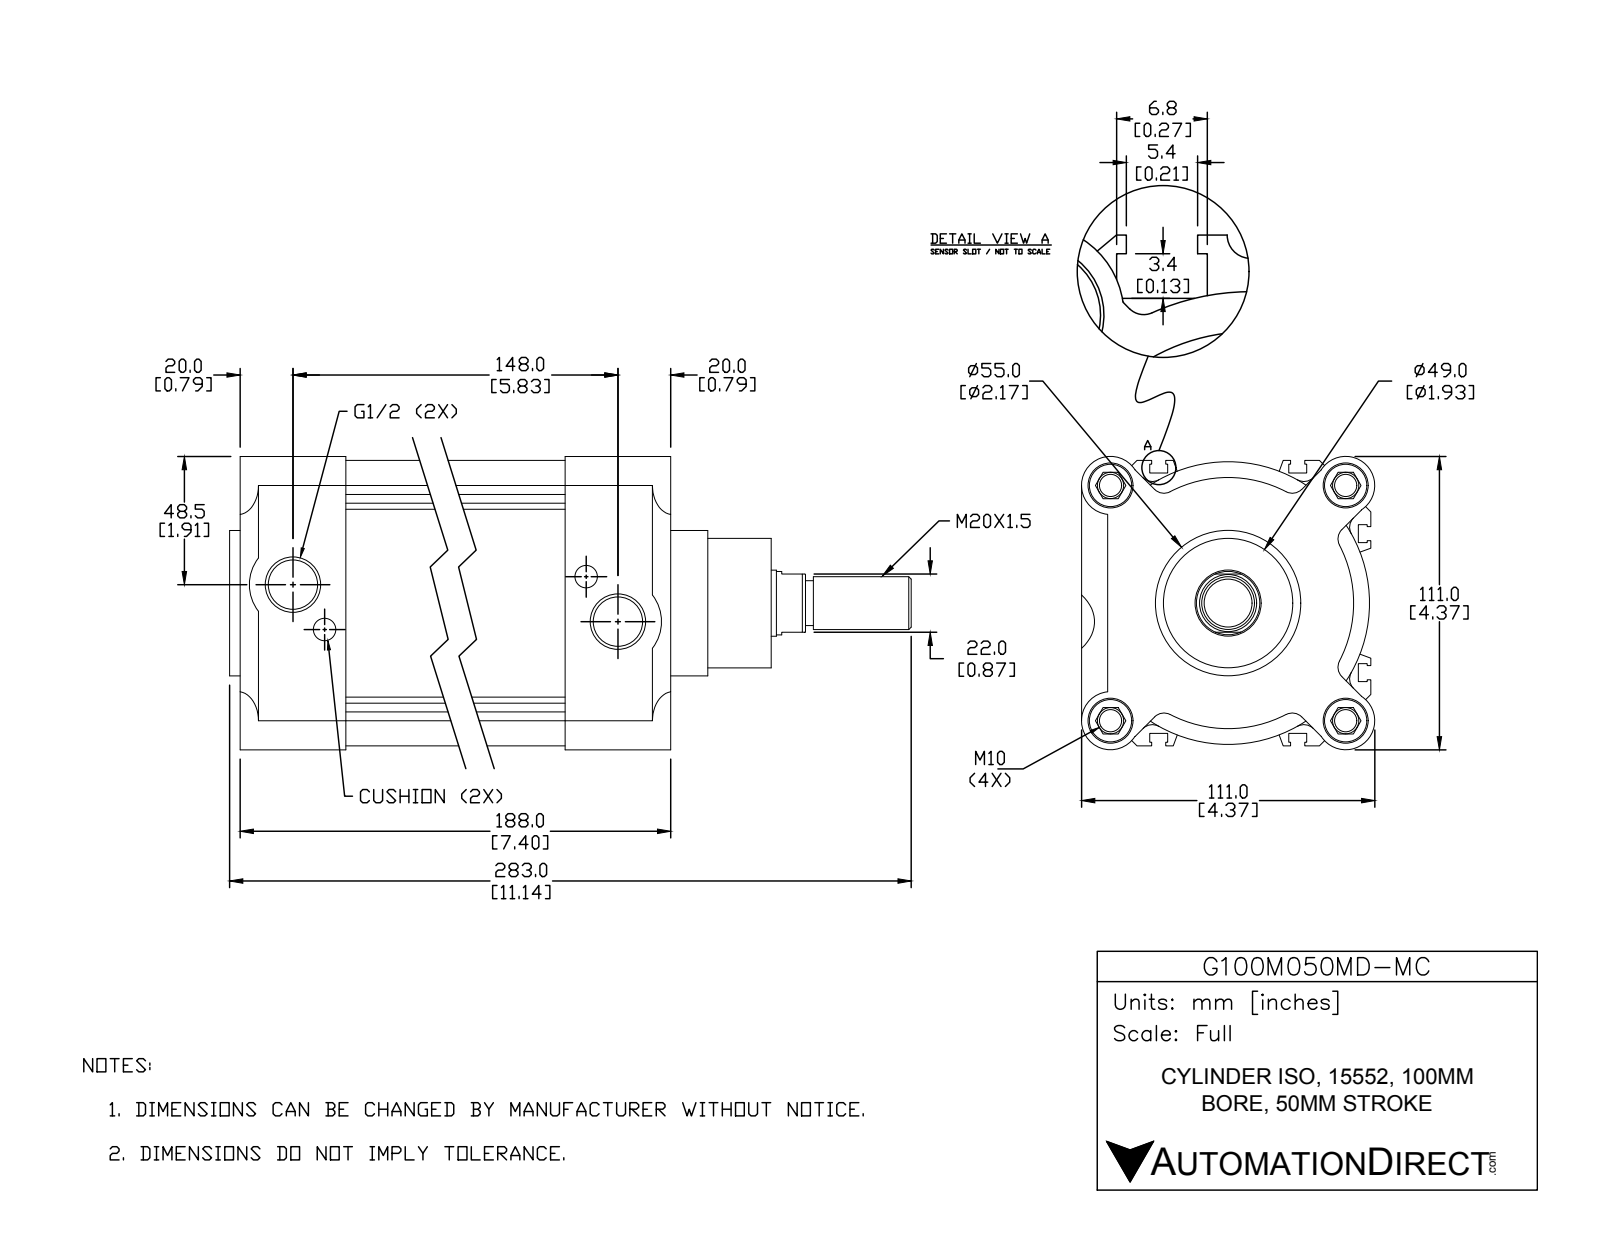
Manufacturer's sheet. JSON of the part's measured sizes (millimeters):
{"part_name": "100-50-120.5-B; 100-HL; G100M050MD-MC; 10012150-R (+1 more)", "step_written_by": "SolidWorks 2015 (CONFIG_CONTROL_DESIGN)", "units": "millimeters", "bodies": {"solids": 4, "faces": 462, "planar": 248, "cylindrical": 162, "other": 52}, "overall_size": [283, 111, 111], "volume_mm3": 1734000, "surface_area_mm2": 266500, "round_holes": [[8.4, 4], [17, 4], [8.5, 2], [18.6, 2], [25, 1]], "round_bosses_or_shafts": [[16, 4], [100, 1], [55, 1], [49, 1], [24, 1], [20, 1], [17, 1]], "partial_cylinders_radius": [[5, 12], [0.1, 6], [9.5, 4], [11, 4], [16.5, 2], [47.5, 1], [53, 1], [53.5, 1]], "face_to_face_distances": [50, 88, 138, 10, 98, 40, 148, 108, 38, 60], "hole_center_spacings": [62.9, 89, 20.8, 125.9, 136, 125.6, 148.7]}
